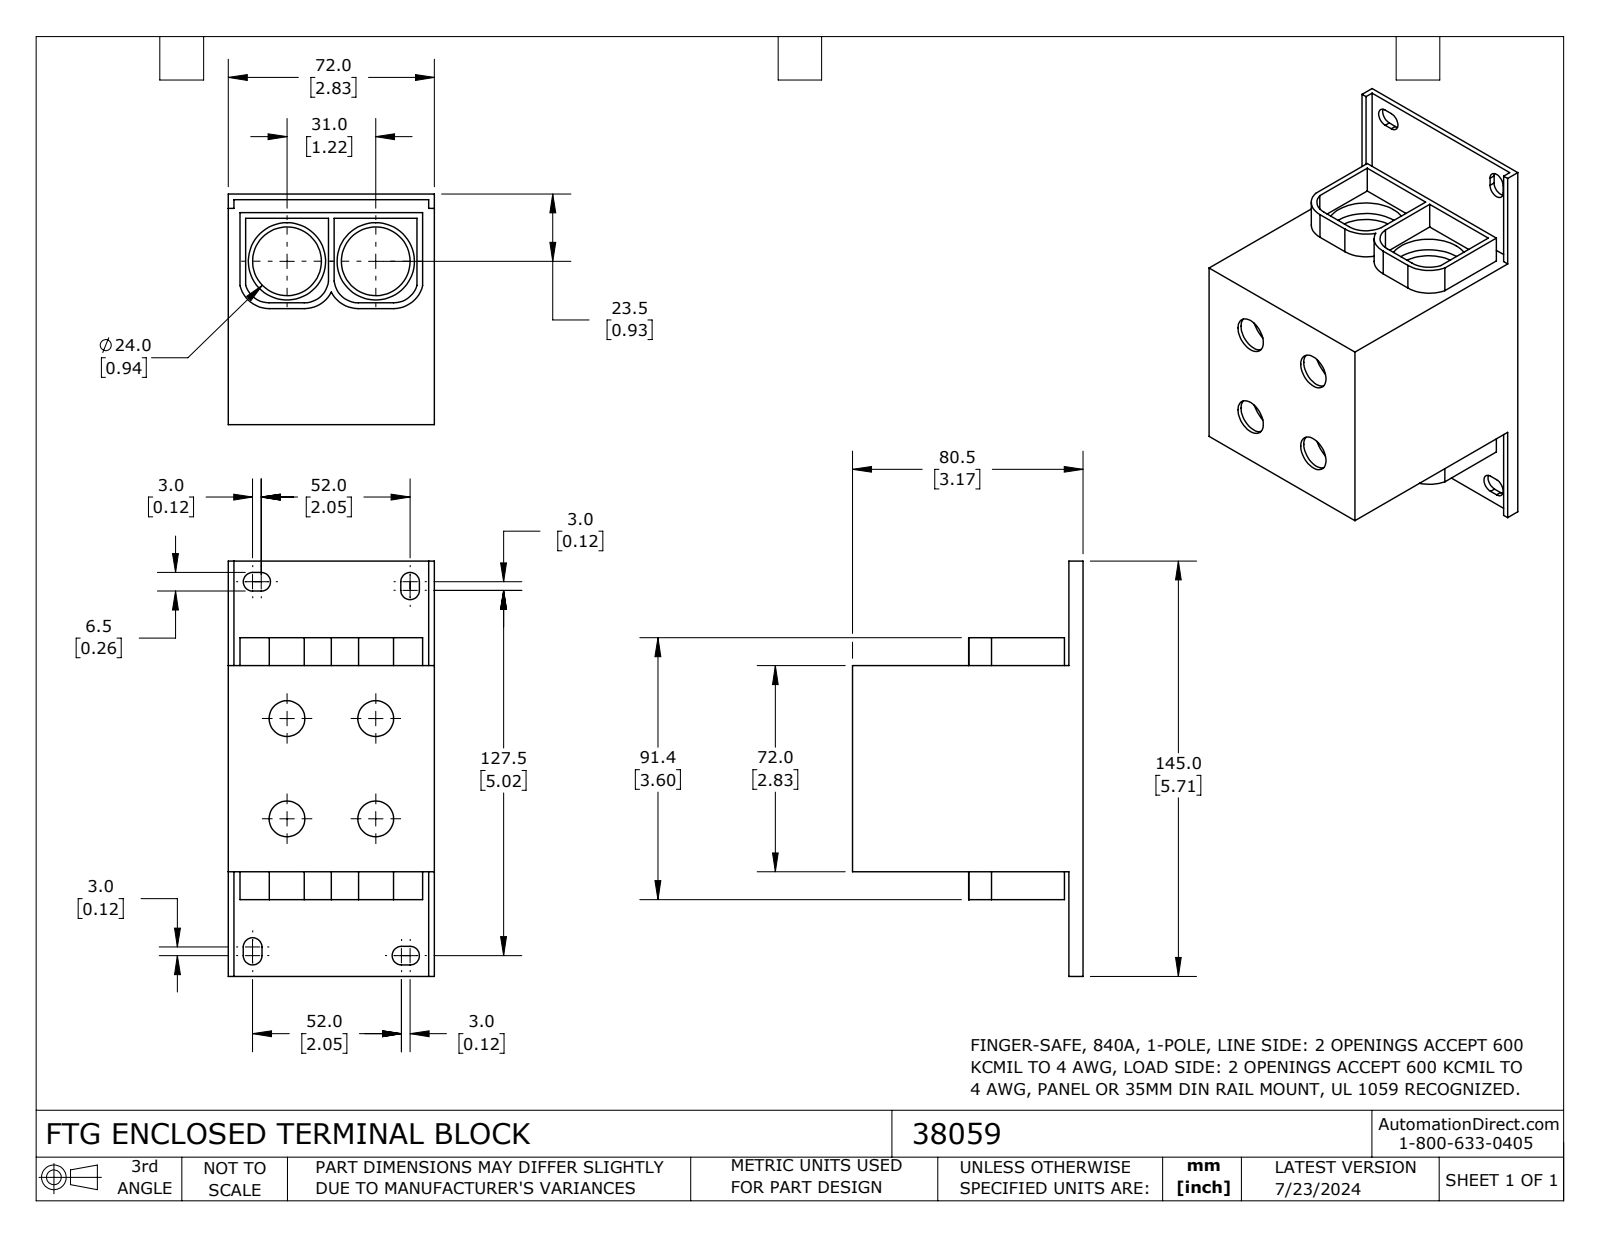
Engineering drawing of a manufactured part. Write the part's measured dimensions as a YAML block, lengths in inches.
part_name: "38059"
step_written_by: "SolidWorks 2023 (CONFIG_CONTROL_DESIGN)"
units: inches
bodies: {solids: 1, faces: 130, planar: 66, cylindrical: 56, other: 8}
overall_size: [5.709, 3.169, 2.835]
volume: 21.65
surface_area: 103
round_holes:
  - {diameter: 0.492, count: 4}
  - {diameter: 0.827, count: 4}
  - {diameter: 0.945, count: 2}
  - {diameter: 1.063, count: 2}
partial_cylinders:
  - {radius: 0.128, count: 8}
  - {radius: 0.335, count: 4}
  - {radius: 0.413, count: 4}
face_to_face_distances: [2.835, 0.079, 3.169, 3.091, 0.256, 1.217, 1.378, 2.913, 1.24, 0.161]
hole_center_spacings: [1.22, 1.378, 1.841]
